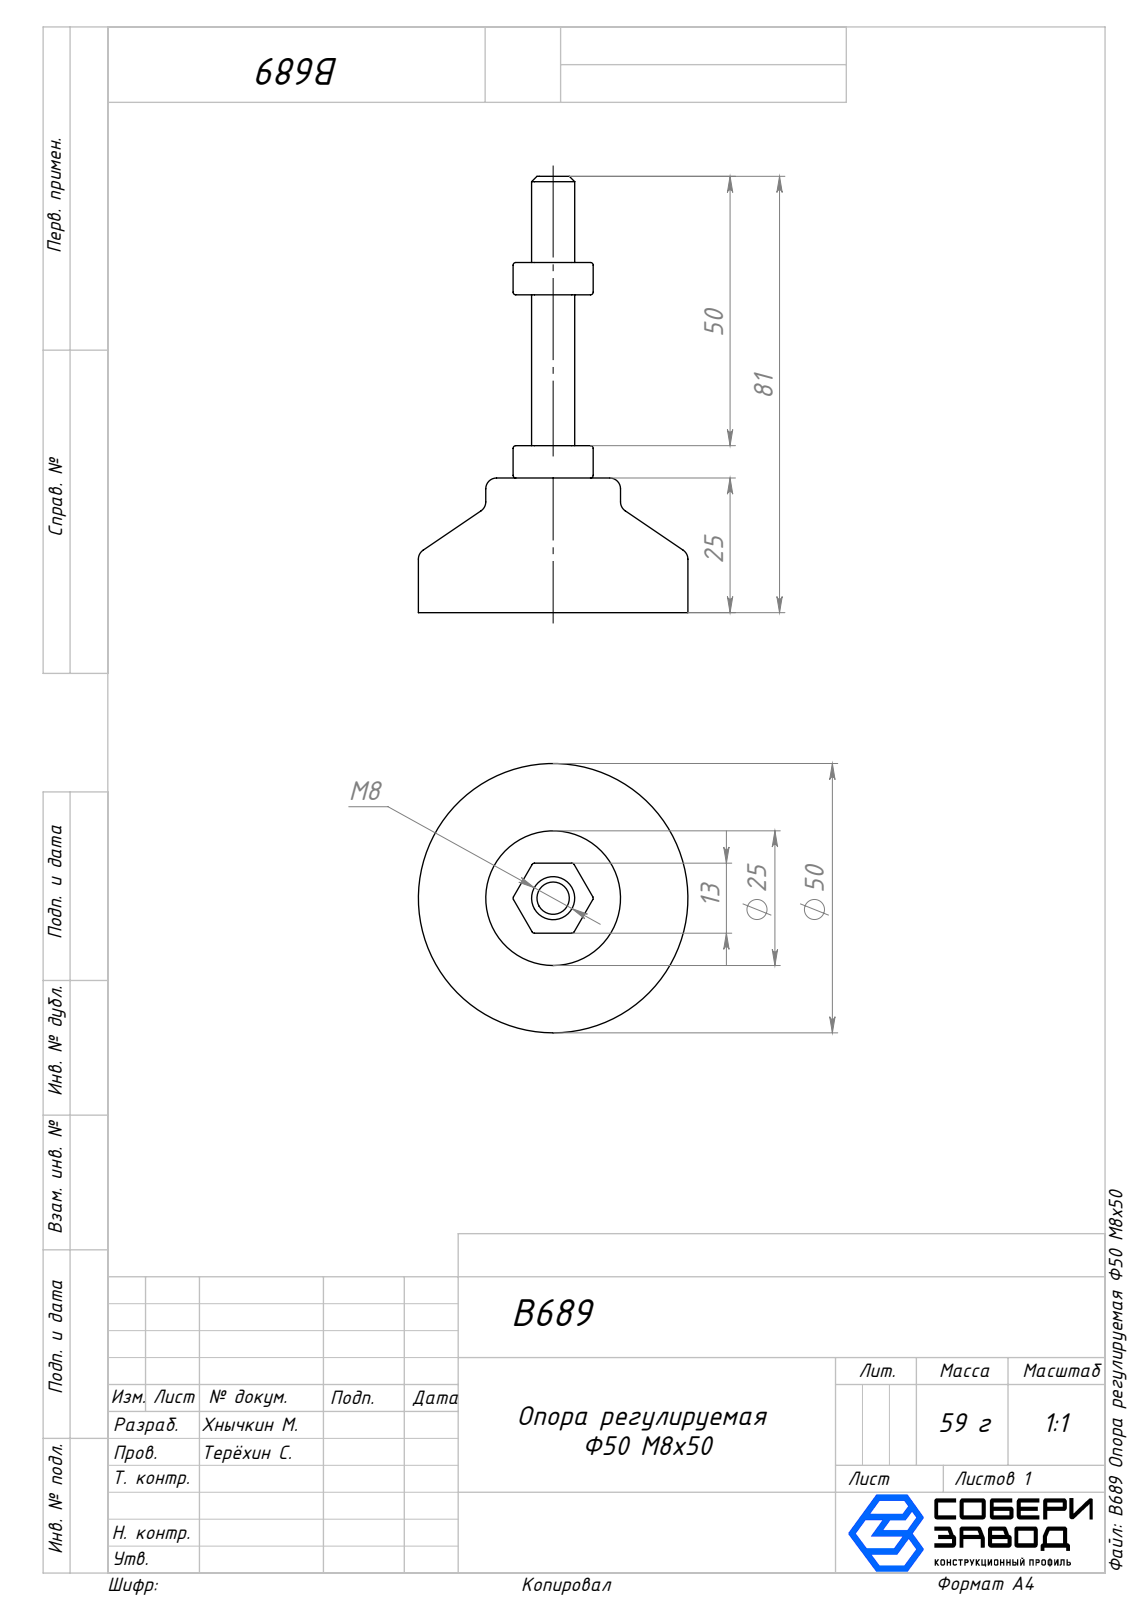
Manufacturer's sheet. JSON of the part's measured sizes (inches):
{"part_name": "Опора_00; Вал_00; B689 Опора регулируемая Ф50 М8х50; Гайка_00 (+1 more)", "step_written_by": "SolidWorks 2025 (AUTOMOTIVE_DESIGN)", "units": "inches", "bodies": {"solids": 4, "faces": 157, "planar": 29, "cylindrical": 70, "other": 58}, "overall_size": [3.189, 1.969, 1.969], "volume_in3": 1.988, "surface_area_in2": 16.36, "round_holes": [[0.157, 1], [0.236, 1], [1.063, 1]], "round_bosses_or_shafts": [[1.969, 1], [0.984, 1], [0.315, 1], [0.197, 1]], "partial_cylinders_radius": [[0.02, 42]], "face_to_face_distances": [0.433, 0.984, 0.551, 0.512, 0.236, 2.323, 1.339, 0.197, 0.748, 2.087]}
